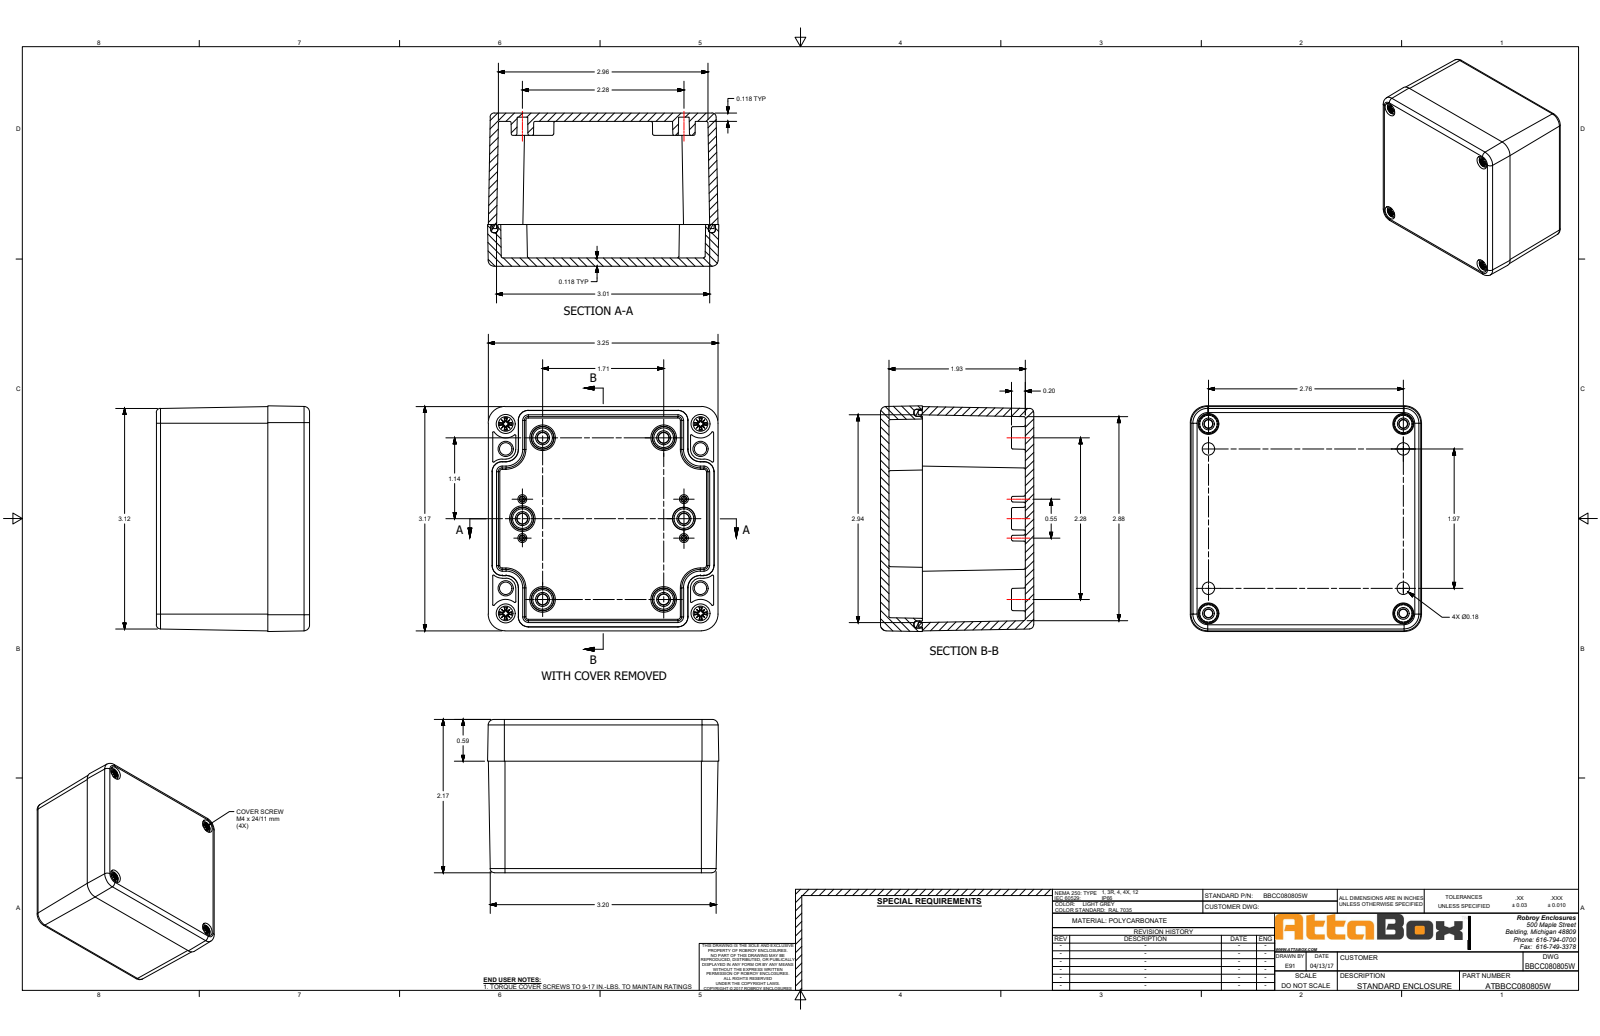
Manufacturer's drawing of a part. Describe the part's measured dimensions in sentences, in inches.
The part is named "BBCC080805W". Its 3-D file was written by "SolidWorks 2018 (AUTOMOTIVE_DESIGN)". It is 11 solids with 1672 faces: 611 planar, 464 cylindrical and 597 other. Overall it measures 3.268 by 3.189 by 2.165 inches. Its volume is 6.423 cubic inches and its surface area 119.6 square inches. Round holes: 4 of diameter 0.128, 4 of diameter 0.177, 4 of diameter 0.193, 4 of diameter 0.197, 4 of diameter 0.201, 4 of diameter 0.276, 4 of diameter 0.287, 4 of diameter 0.295. Round bosses or shafts: 4 of diameter 0.268, 4 of diameter 0.173, 4 of diameter 0.157, 4 of diameter 0.13. Partial cylindrical surfaces (rounded edges, fillets, slot ends): 32 of radius 0.039, 24 of radius 0.012, 16 of radius 0.02, 12 of radius 0.197, 8 of radius 0.098, 4 of radius 0.059, 4 of radius 0.079, 4 of radius 0.102. The main face-to-face distances are 0.118, 2.047, 2.165, 1.929, 1.575, 0.37, 0.472, 1.457, 0.591, 3.179. The hole center spacings are 0.354, 2.323, 2.756, 2.779, 3.604, 1.969, 2.677, 3.387.
